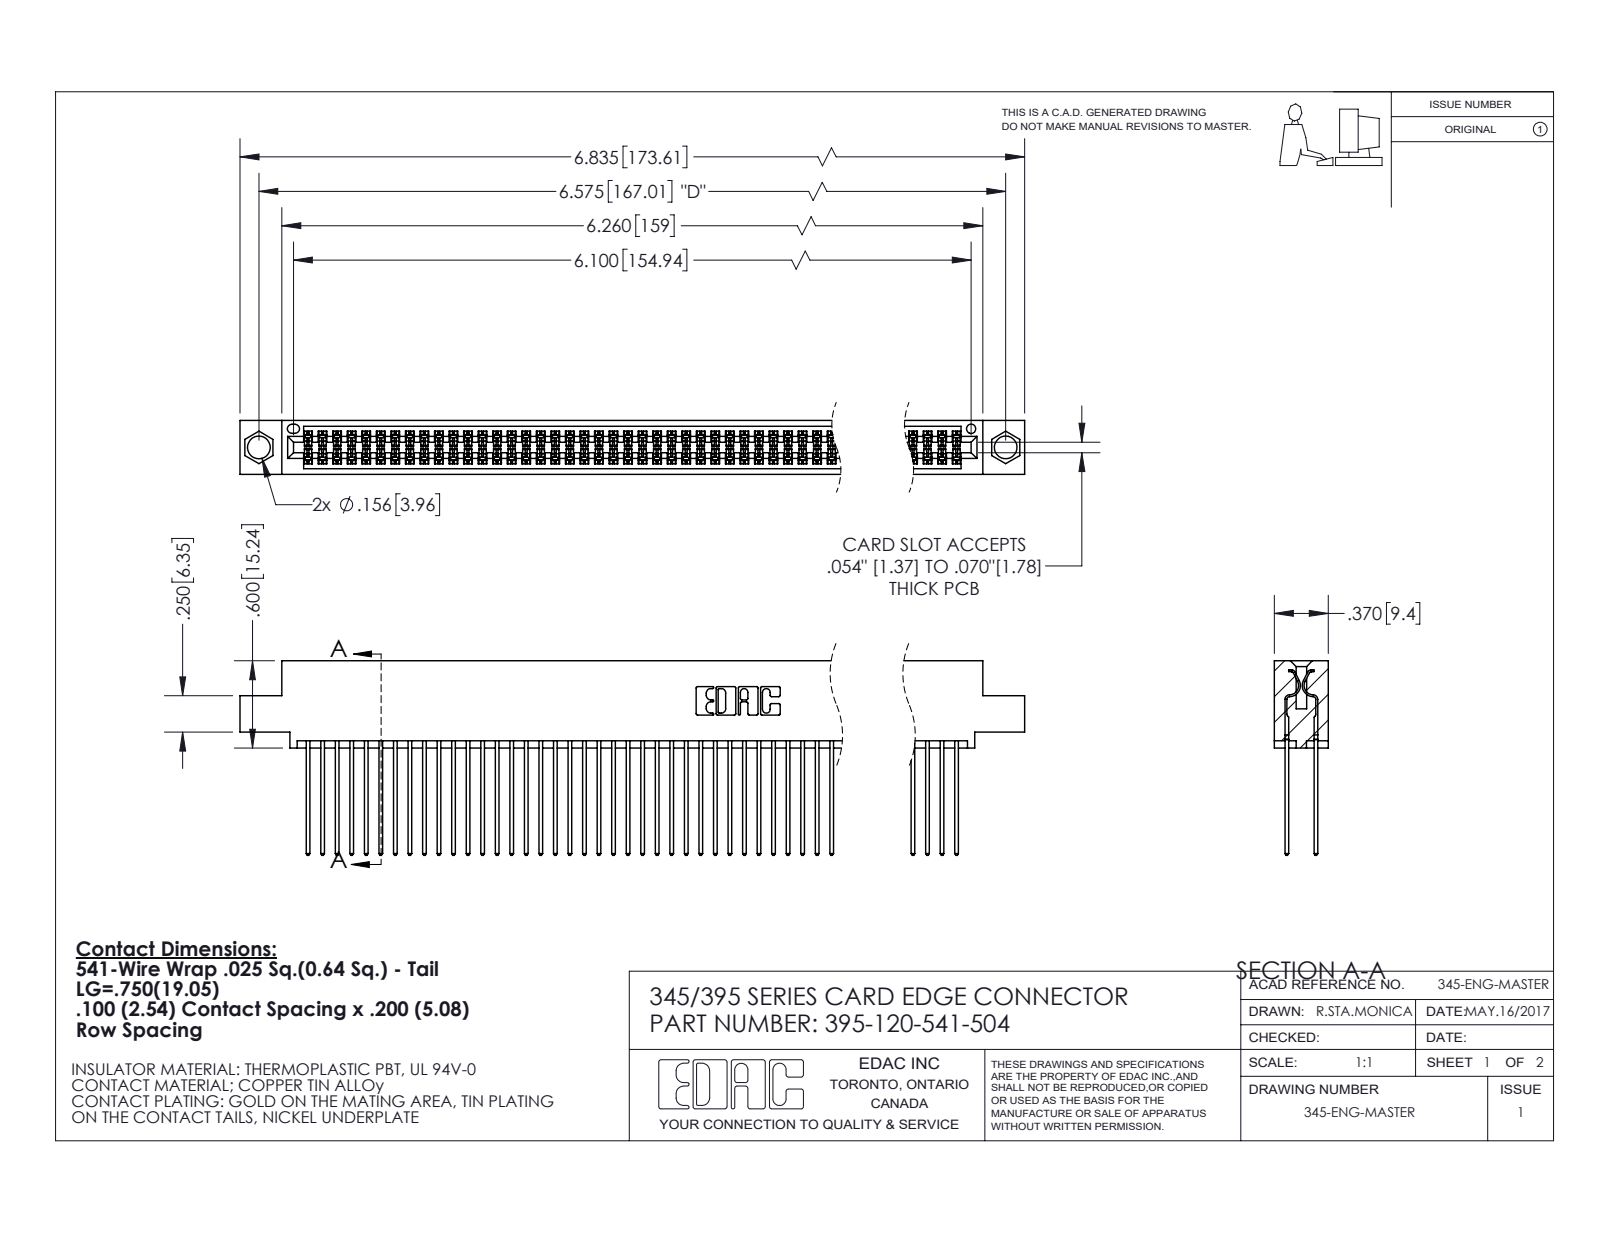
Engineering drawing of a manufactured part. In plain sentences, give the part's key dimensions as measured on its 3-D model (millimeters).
The part is named "345-292-001_345-293-141; 345 Part_0.110 Offset - 0.156 Dia-TI; 395-120-541-504". Its 3-D file was written by "SolidWorks 2020 (CONFIG_CONTROL_DESIGN)". It is 121 solids with 6144 faces: 4058 planar, 2086 cylindrical and 0 other. Overall it measures 173.6 by 34 by 9.4 millimeters. Its volume is 17 530 cubic millimeters and its surface area 29 460 square millimeters. Round holes: 2 of diameter 4, 1 of diameter 1.6. Partial cylindrical surfaces (rounded edges, fillets, slot ends): 180 of radius 0.2, 120 of radius 0.3, 22 of radius 0.3, 6 of radius 0.2, 6 of radius 0.8, 3 of radius 0.7, 2 of radius 0.4, 2 of radius 0.5. The main face-to-face distances are 7.6, 1.8, 5.1, 2.5, 6.9, 0.6, 5.7, 9.4, 4.4, 3.8. The hole center spacings are 6.9, 161, 167.
